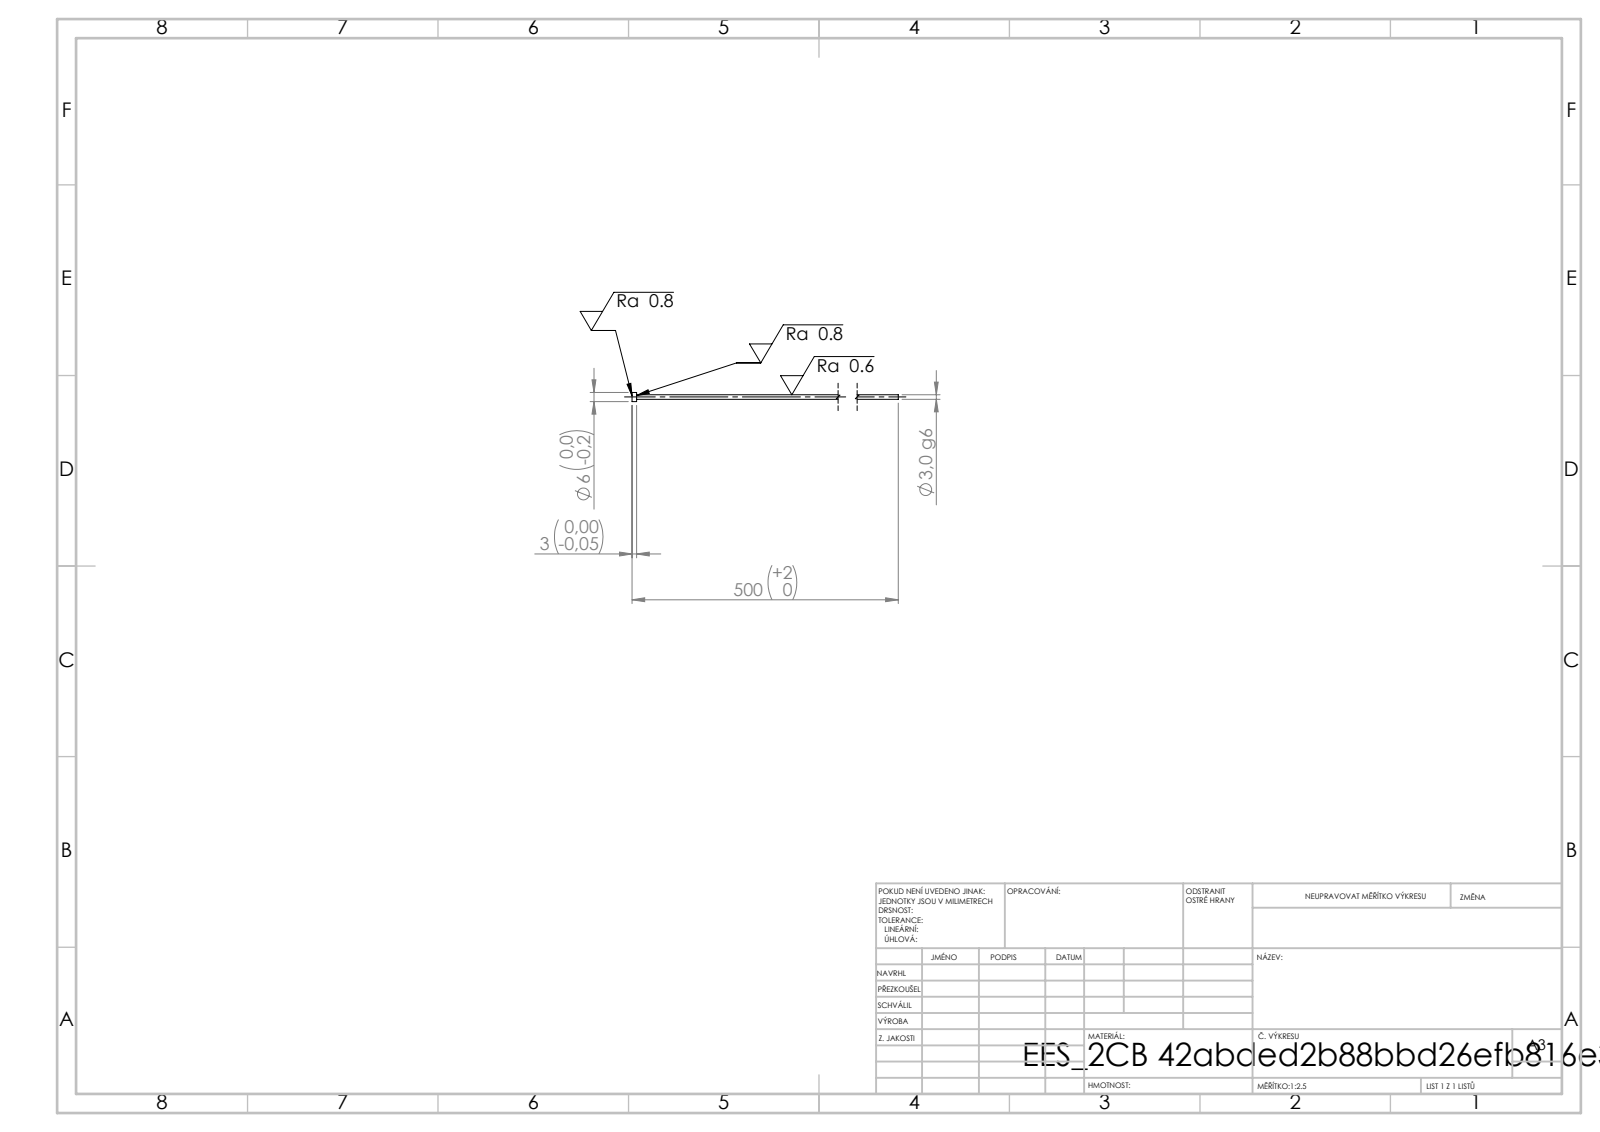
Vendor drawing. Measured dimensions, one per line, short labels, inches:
written by: SolidWorks 2019 (CONFIG_CONTROL_DESIGN)
unit: in
bodies: 1 solid, 7 faces (3 planar, 4 cylindrical, 0 other)
size: 19.685 × 0.236 × 0.236
volume: 0.22 in³; area: 7.435 in²
bosses: 1× ⌀0.236, 1× ⌀0.118
face distances: 0.118, 19.685, 19.567
